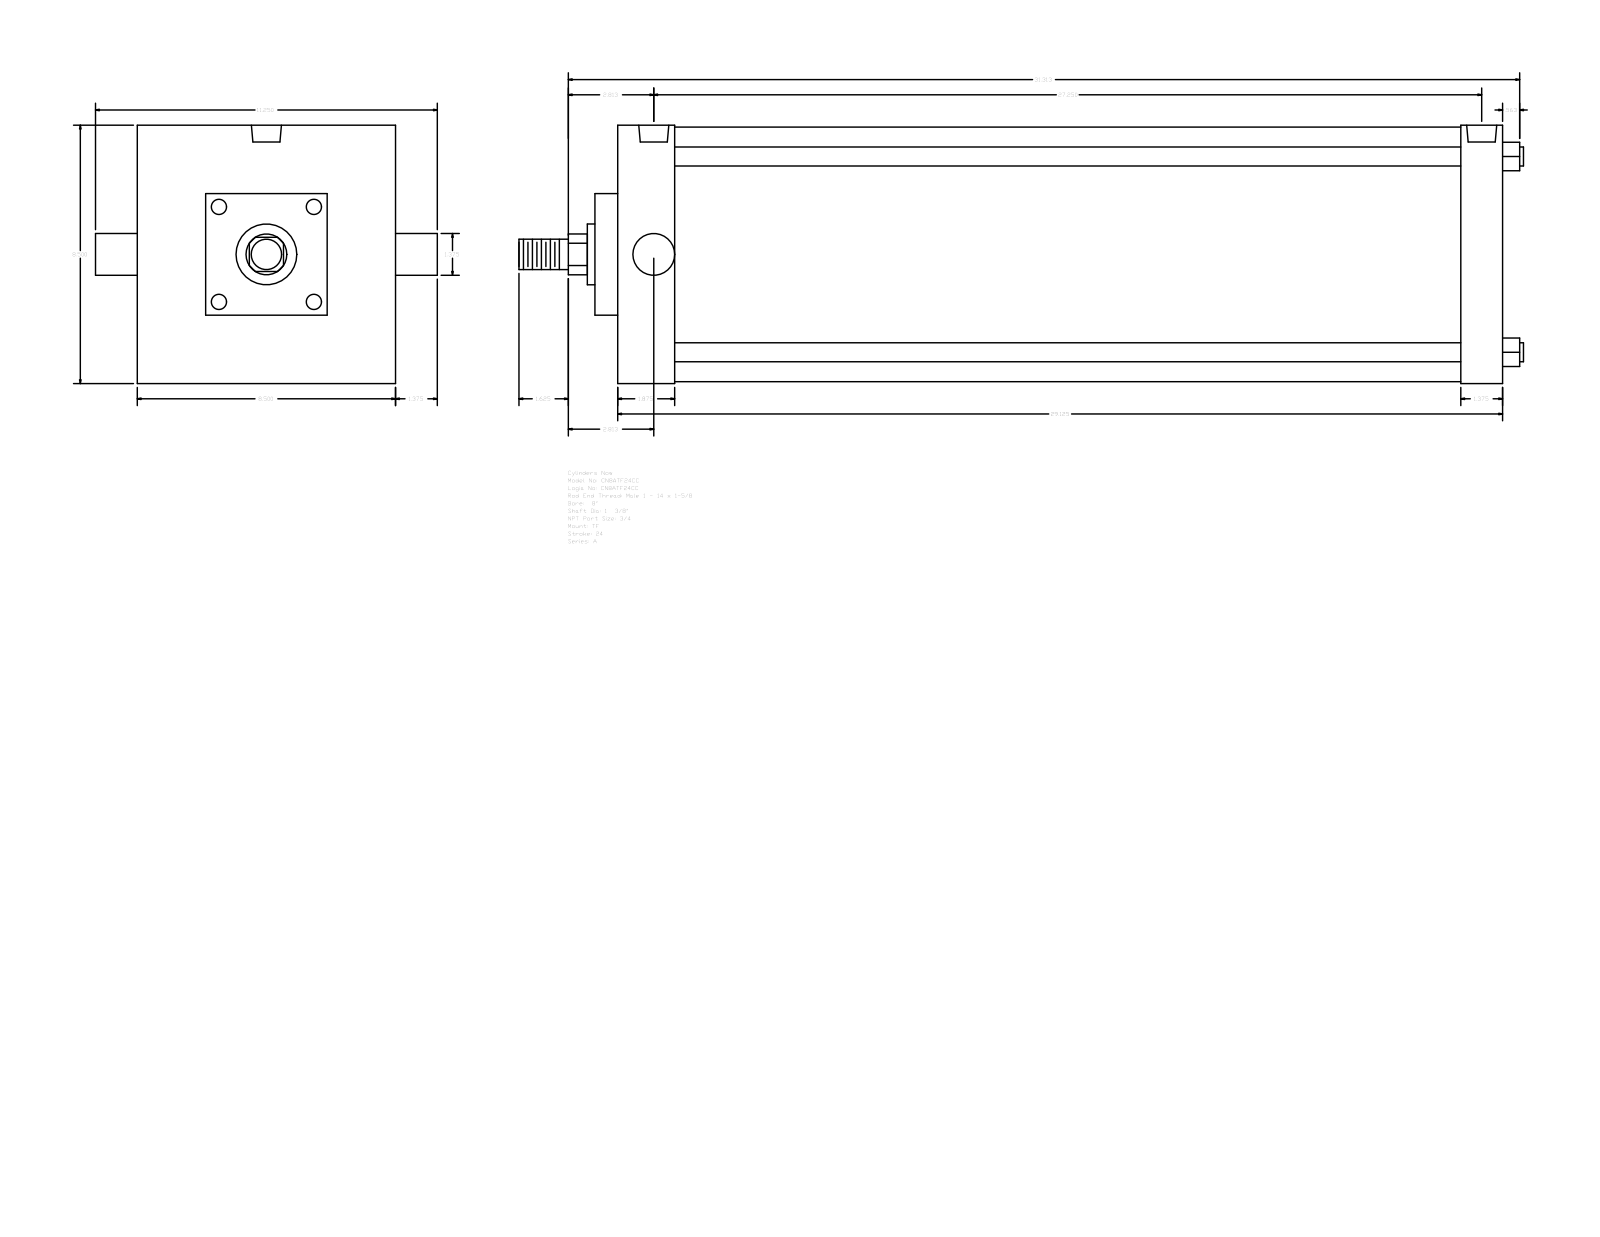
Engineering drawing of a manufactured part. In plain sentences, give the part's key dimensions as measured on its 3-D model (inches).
The part is named "A_TF__0800_1.375". Its 3-D file was written by "GSSL Pune (CONFIG_CONTROL_DESIGN)". It is 0 solids with 89 faces: 65 planar, 24 cylindrical and 0 other. Overall it measures 33.063 by 11.25 by 8.5 inches. Round holes: 3 of diameter 0.594, 2 of diameter 0.989. Round bosses or shafts: 4 of diameter 0.625, 2 of diameter 1.375, 1 of diameter 8.375, 1 of diameter 2, 1 of diameter 1. Partial cylindrical surfaces (rounded edges, fillets, slot ends): 1 of radius 0.672. The main face-to-face distances are 29.125, 8.5, 1.375, 1.875, 27.25, 27.75, 25.875, 0.75, 2.625, 28.5. The hole center spacings are 0.25, 27, 26.75, 27.25.
